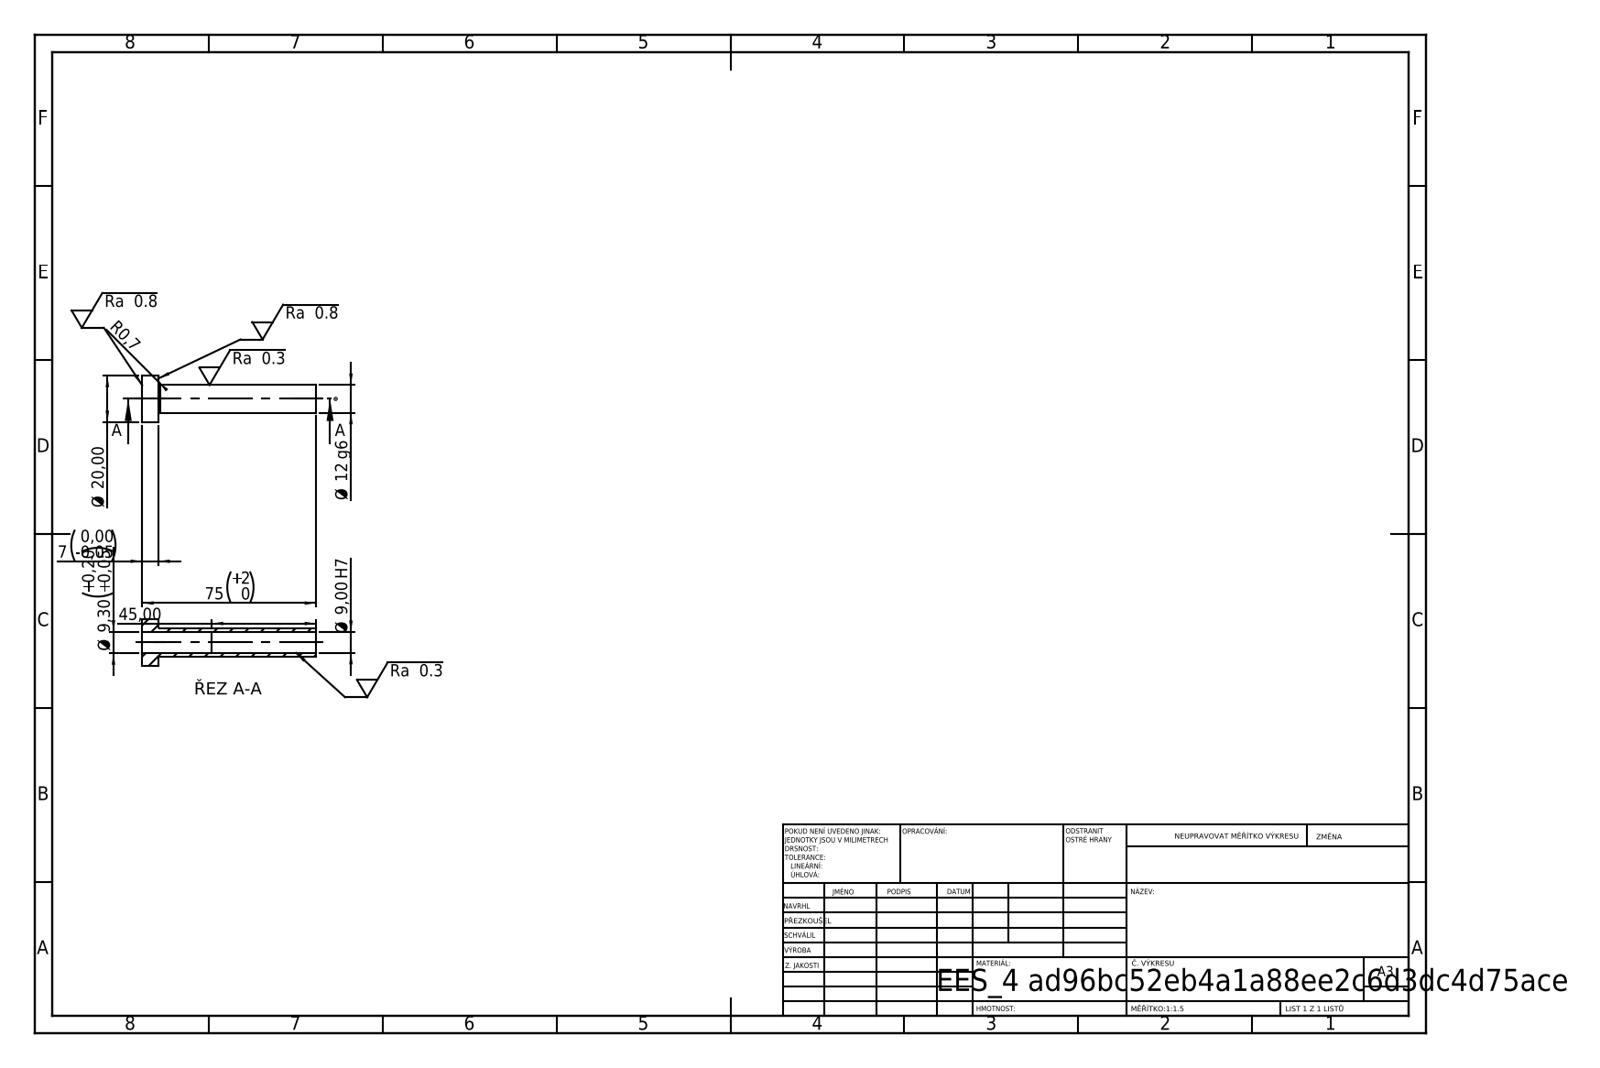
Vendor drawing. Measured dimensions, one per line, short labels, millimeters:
written by: SolidWorks 2019 (CONFIG_CONTROL_DESIGN)
unit: mm
bodies: 1 solid, 14 faces (4 planar, 8 cylindrical, 2 other)
size: 75 × 20 × 20
volume: 4 993 mm³; area: 5 642 mm²
holes: 1× ⌀9, 1× ⌀9.3
bosses: 1× ⌀20, 1× ⌀12
face distances: 7, 75, 68, 30, 23, 45
